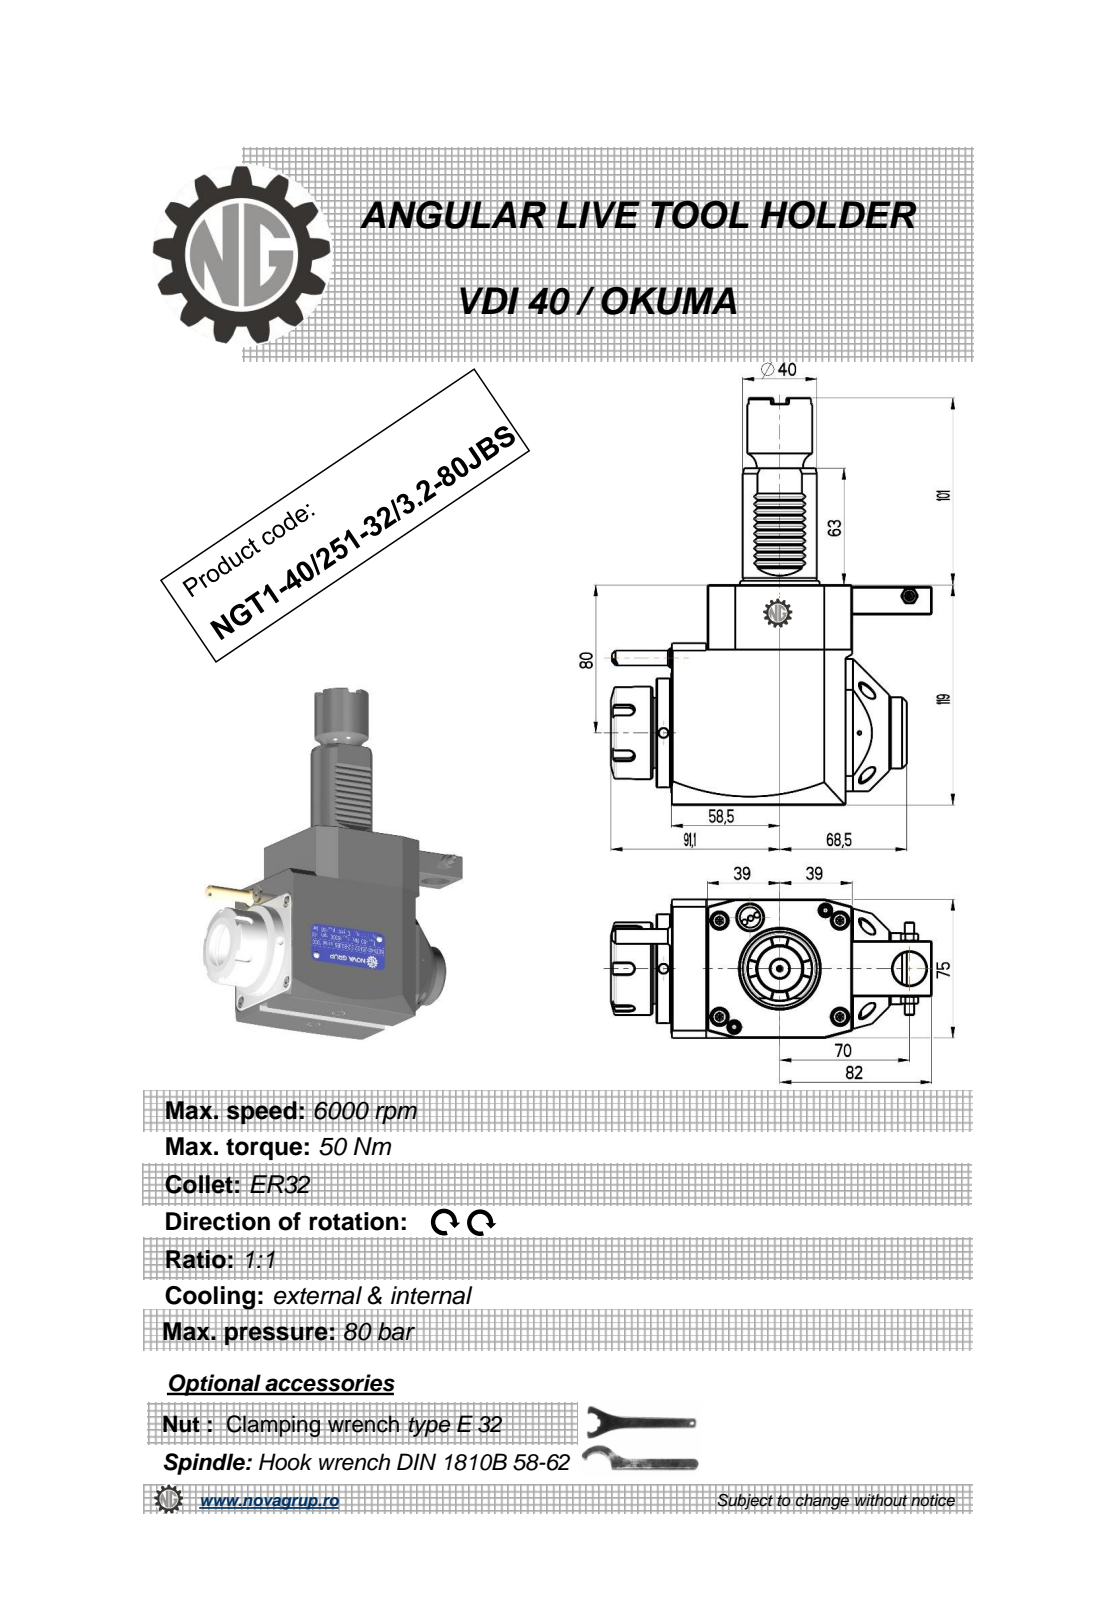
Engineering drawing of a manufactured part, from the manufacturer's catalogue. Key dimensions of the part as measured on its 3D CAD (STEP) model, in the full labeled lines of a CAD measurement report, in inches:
Part name (STEP PRODUCT): NGT1_40_251_32_3_2_80JBS
STEP written by: PRO/ENGINEER BY PARAMETRIC TECHNOLOGY CORPORATION, 2010280 (CONFIG_CONTROL_DESIGN)
Units: inches
Bodies: 1 solid, 497 faces (226 planar, 97 cylindrical, 174 other)
Overall size (bounding box): 8.661 × 6.815 × 2.953
Volume: 64.5 in³ · Surface area: 134 in²
Round holes (diameter × count): ⌀0.197 ×3, ⌀0.118 ×1, ⌀0.165 ×1, ⌀0.374 ×1, ⌀0.709 ×1, ⌀0.984 ×1, ⌀1.063 ×1, ⌀1.811 ×1
Round bosses / shafts (diameter × count): ⌀2.323 ×1, ⌀1.969 ×1, ⌀1.811 ×1, ⌀1.614 ×1, ⌀1.575 ×1, ⌀1.516 ×1, ⌀1.378 ×1, ⌀0.394 ×1
Partial cylindrical surfaces — rounded edges, fillets, slot ends (radius × count): R0.01 ×12, R0.012 ×10, R0.008 ×6, R0.118 ×5, R0.228 ×2, R0.236 ×2, R23.622 ×2, R0.02 ×1
Main face-to-face distances: 2.953, 4.685, 0.768, 3.839, 3.071, 0.76, 3.831, 1.083, 0.039, 0.138
Hole centre spacings: 1.436, 1.737, 2.47, 2.756, 2.854, 5.226, 5.983
